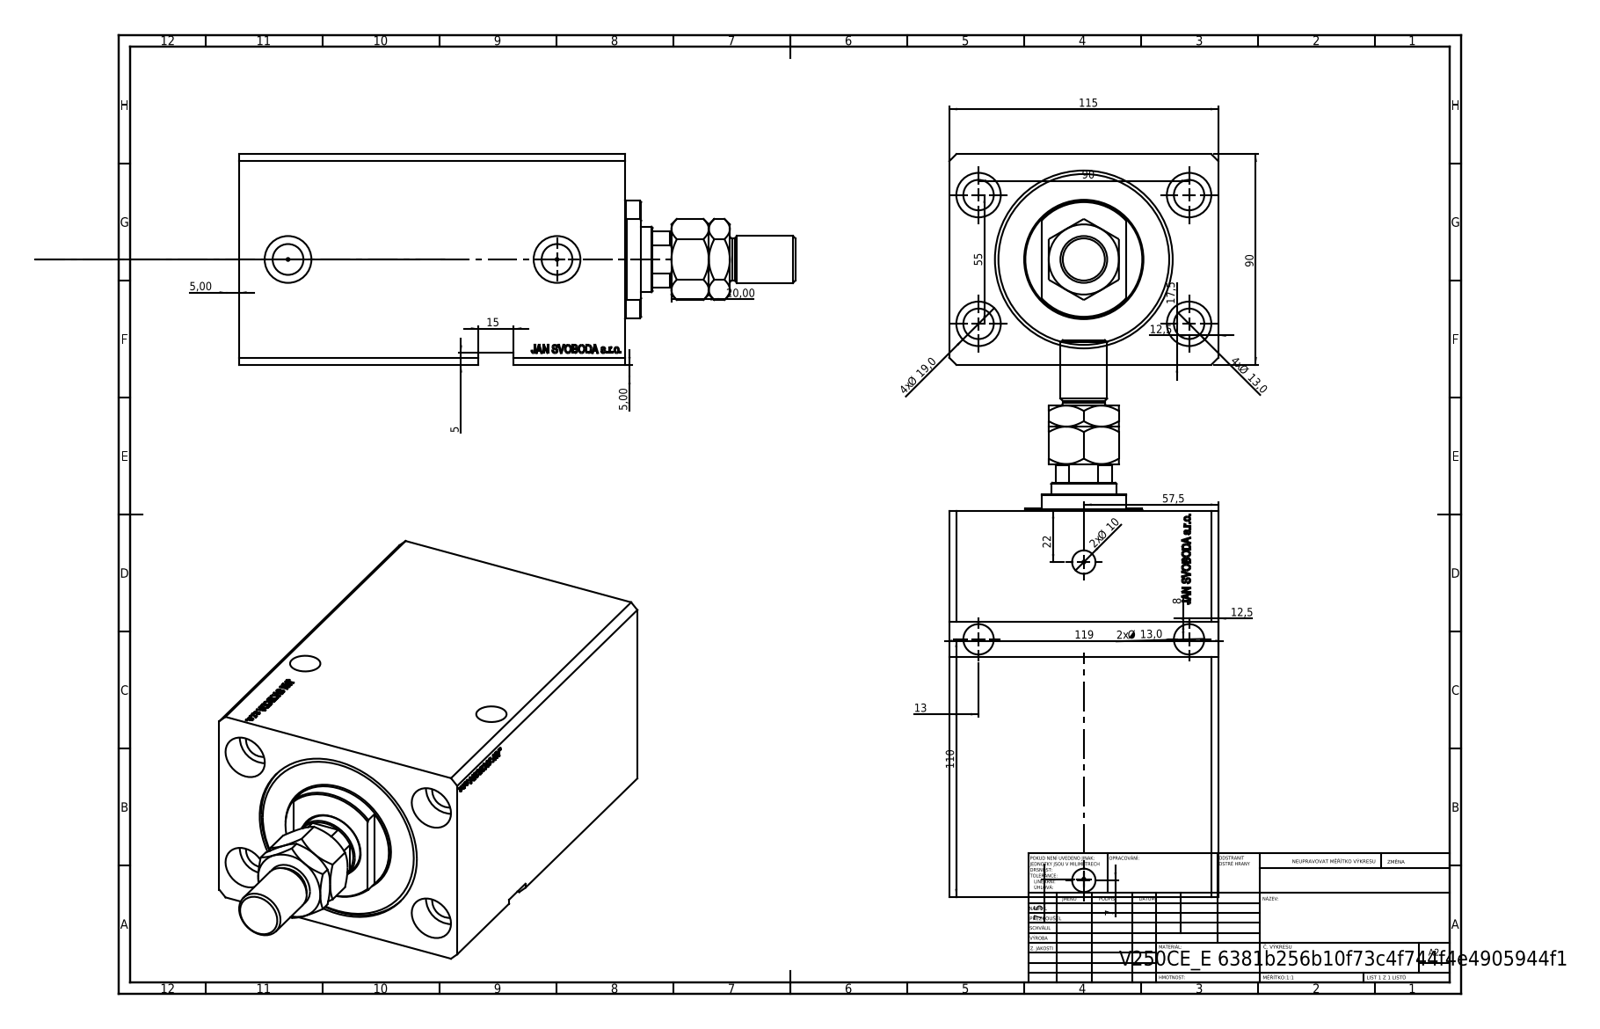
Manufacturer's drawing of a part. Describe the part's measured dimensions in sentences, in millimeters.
The part is named "V250CE_C_VCP; MTA; V250CE_VC_E; V250CE_E_Body". Its 3-D file was written by "SolidWorks 2019 (CONFIG_CONTROL_DESIGN)". It is 4 solids with 986 faces: 482 planar, 88 cylindrical and 416 other. Overall it measures 237.9 by 115 by 90 millimeters. Its volume is 1 409 000 cubic millimeters and its surface area 203 733 square millimeters. Round holes: 6 of diameter 13, 4 of diameter 1.25, 4 of diameter 19, 2 of diameter 10, 2 of diameter 13.16, 2 of diameter 20, 1 of diameter 18.5, 1 of diameter 28, 1 of diameter 63, 1 of diameter 76. Round bosses or shafts: 1 of diameter 50, 1 of diameter 20, 1 of diameter 18. Partial cylindrical surfaces (rounded edges, fillets, slot ends): 1 of radius 13.5. The main face-to-face distances are 90, 115, 165, 17.9, 147.1, 117, 134.9, 30.1, 54.9, 80. The hole center spacings are 52.74, 90, 55, 55.8, 105.48, 111.92, 112.4, 0.53.
